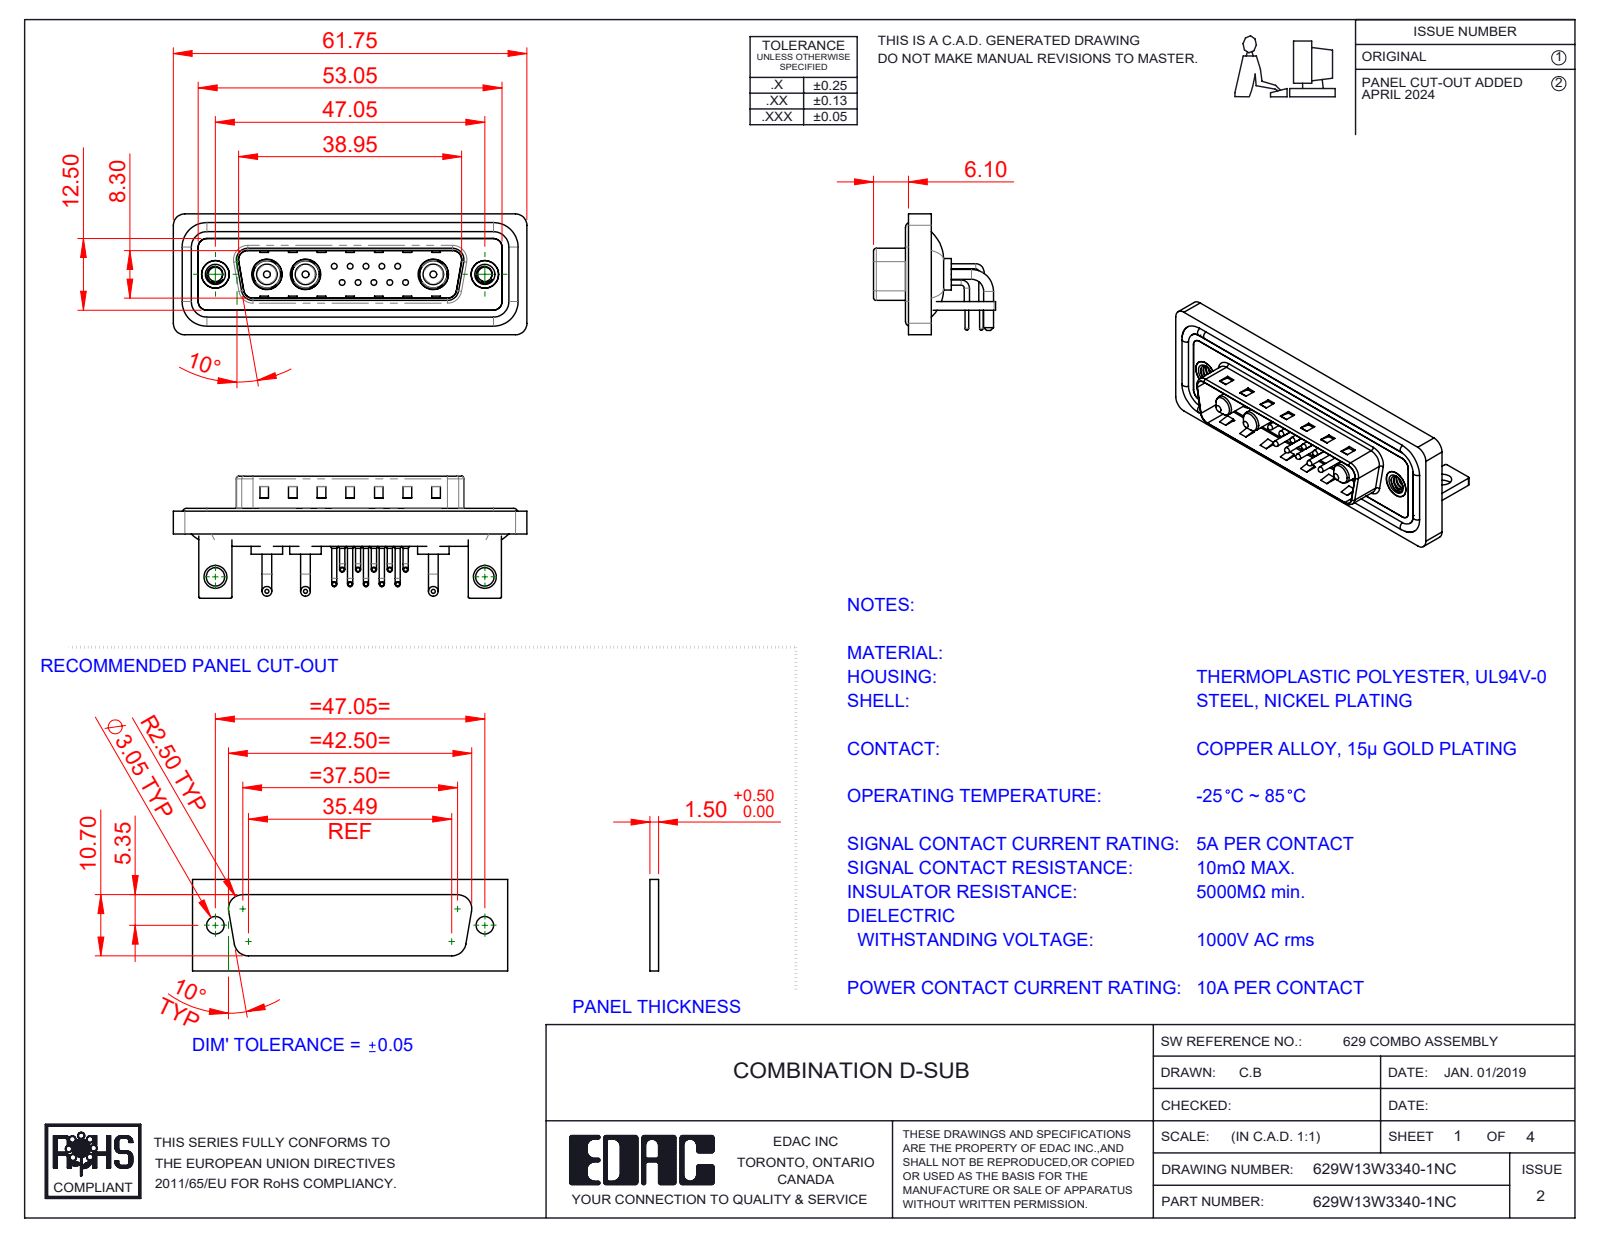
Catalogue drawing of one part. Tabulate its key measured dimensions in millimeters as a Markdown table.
| quantity | value |
| --- | --- |
| part name | 629Combo Contact Row 2; 629Combo Contact Row 1; 629Combo Shell Rear_25 Contacts; 629W13W3340-1NC (+6 more) |
| STEP written by | SolidWorks 2023 (CONFIG_CONTROL_DESIGN) |
| units | millimeters |
| bodies | 25 solids, 1750 faces (899 planar, 629 cylindrical, 222 other) |
| overall size | 61.75 × 21.3 × 21.1 |
| volume | 7 708 mm³ |
| surface area | 12 932 mm² |
| round holes (diameter × count) | 0.75 × 10, 1.6 × 10, 2 × 10, 4.85 × 3, 5.3 × 3, 2.5 × 2, 3.2 × 2, 4 × 2, 4.8 × 2, 5 × 2 |
| round bosses / shafts (diameter × count) | 0.9 × 20, 1.5 × 10, 1 × 10, 0.65 × 10, 1.7 × 6, 1.6 × 4, 5.5 × 3, 5.2 × 3 |
| partial cylindrical surfaces (radius × count) | 2 × 19, 1.5 × 18, 0.25 × 16, 1.01 × 10, 0.5 × 9, 1.6 × 8, 0.6 × 4, 0.65 × 4 |
| main face-to-face distances | 0.4, 1.5, 0.8, 2.9, 2.1, 1.1, 4.1, 1.6, 3.7, 4.5 |
| hole center spacings | 3.16, 2.77, 5.04, 5.54, 7.49, 5.03, 8.31, 10.11 |
